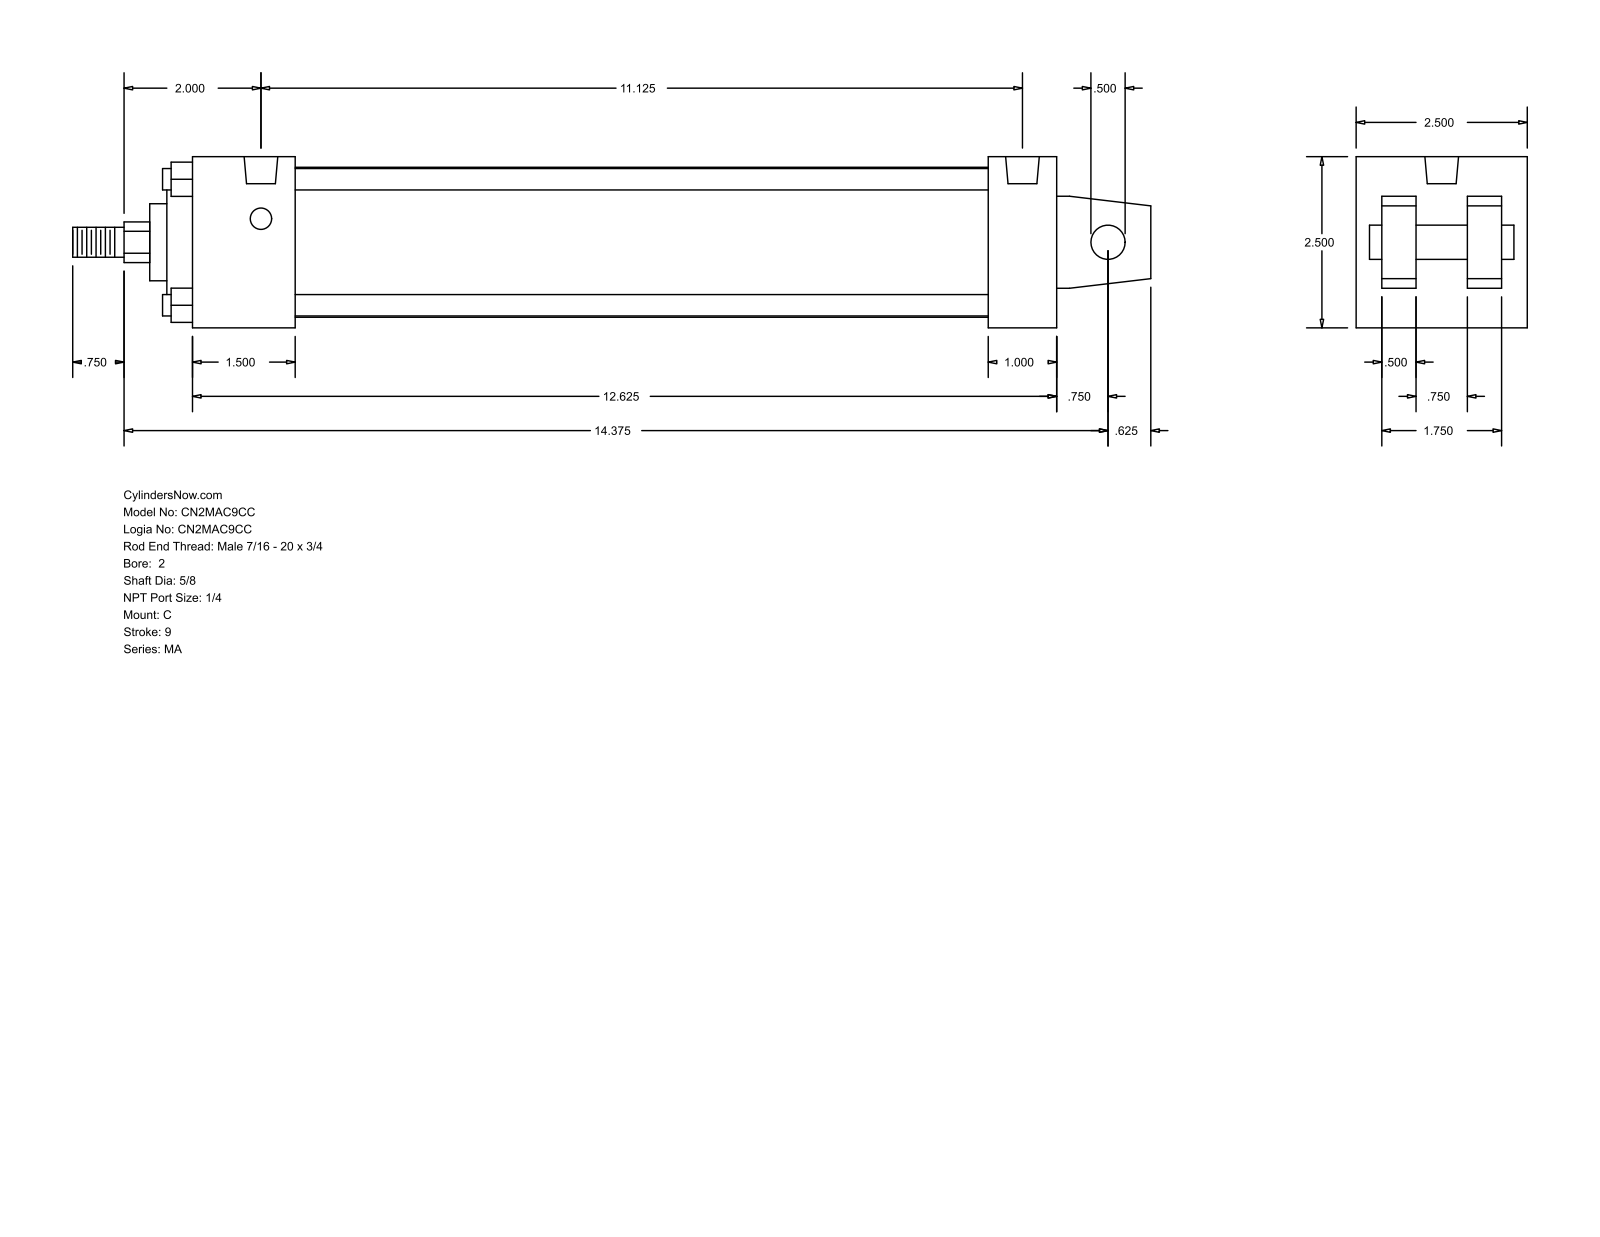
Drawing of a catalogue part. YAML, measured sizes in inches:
part_name: "MA_C__0200_0.625"
step_written_by: "GSSL Pune (CONFIG_CONTROL_DESIGN)"
units: inches
bodies: {solids: 0, faces: 105, planar: 77, cylindrical: 28, other: 0}
overall_size: [15.75, 2.5, 2.5]
round_holes:
  - {diameter: 0.313, count: 4}
  - {diameter: 0.492, count: 2}
round_bosses_or_shafts:
  - {diameter: 0.313, count: 4}
  - {diameter: 2.19, count: 1}
  - {diameter: 2, count: 1}
  - {diameter: 1.125, count: 1}
  - {diameter: 0.625, count: 1}
  - {diameter: 0.5, count: 1}
  - {diameter: 0.437, count: 1}
partial_cylinders:
  - {radius: 0.297, count: 1}
face_to_face_distances: [2.5, 0.375, 0.5, 0.875, 1.625, 2.125, 1.25, 1.5, 12.625, 11.125]
hole_center_spacings: [11.125]
